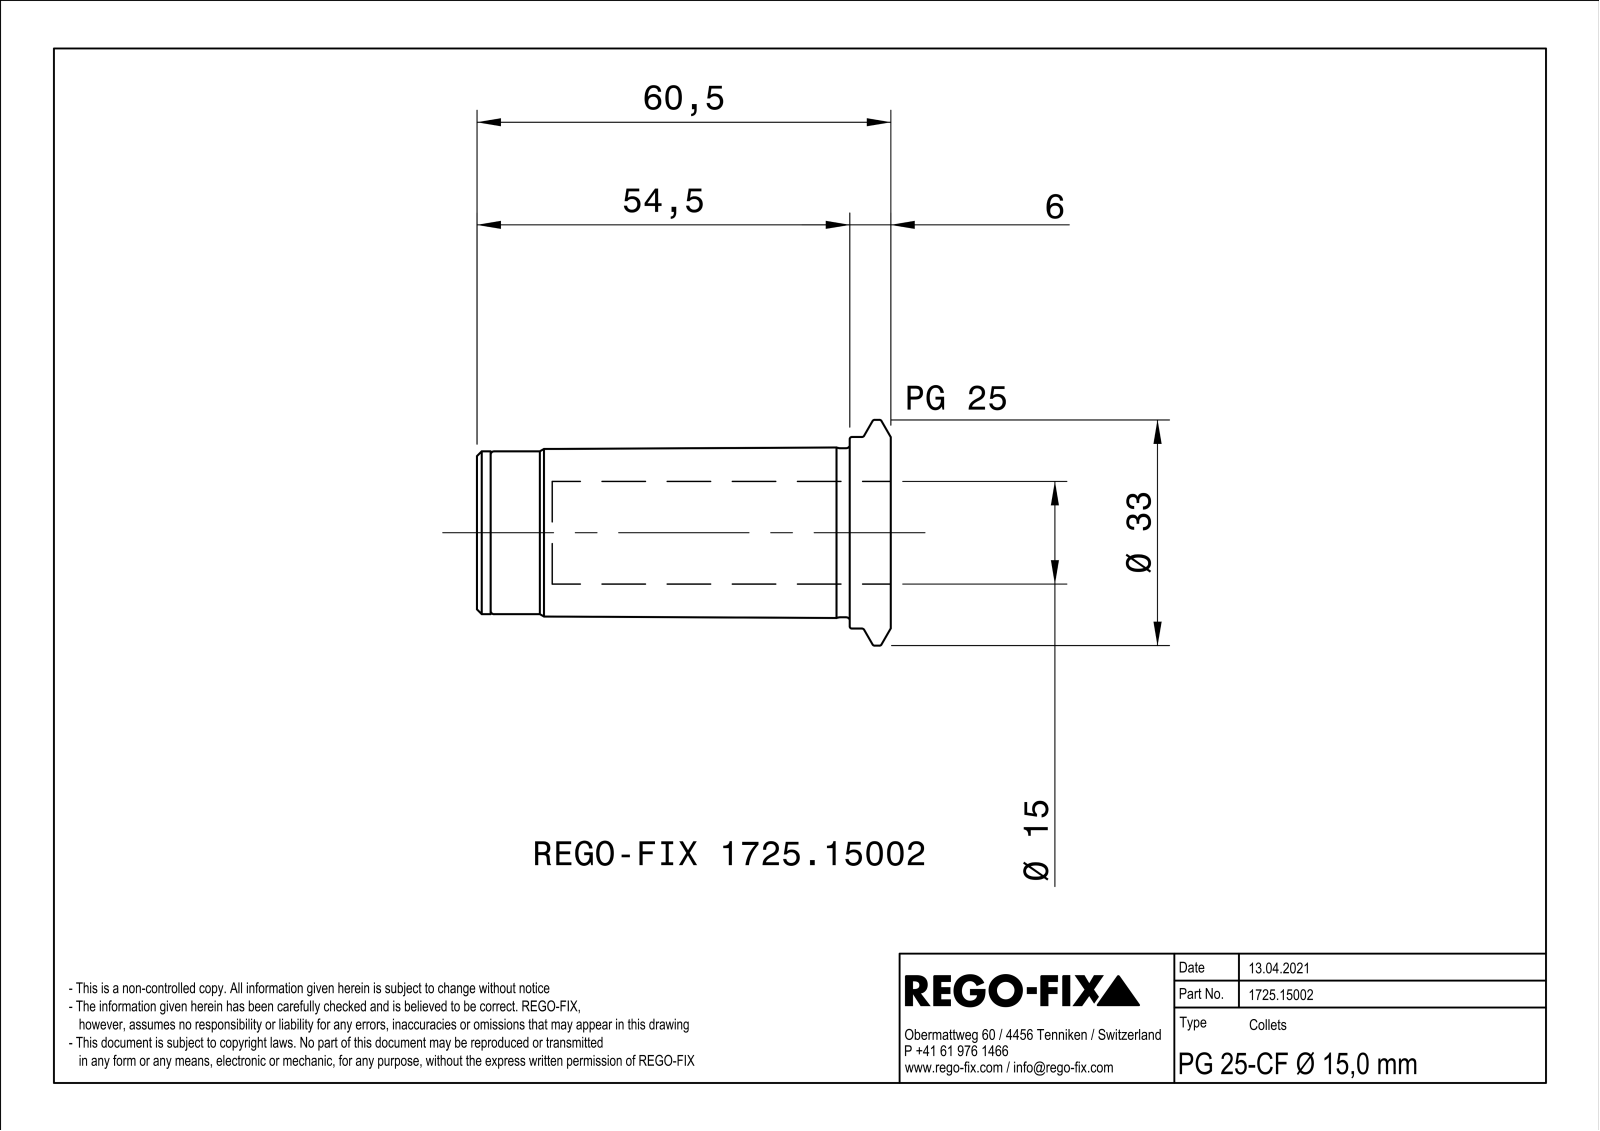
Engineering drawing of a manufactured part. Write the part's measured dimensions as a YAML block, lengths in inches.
part_name: "NOCUT"
step_written_by: "SIEMENS PLM Software Solid Edge ST10 (AUTOMOTIVE_DESIGN)"
units: inches
bodies: {solids: 1, faces: 89, planar: 23, cylindrical: 27, other: 39}
overall_size: [2.382, 1.299, 1.299]
volume: 1.173
surface_area: 17.36
round_holes:
  - {diameter: 0.098, count: 3}
  - {diameter: 0.205, count: 1}
  - {diameter: 0.272, count: 1}
  - {diameter: 0.323, count: 1}
  - {diameter: 0.591, count: 1}
  - {diameter: 0.824, count: 1}
  - {diameter: 0.874, count: 1}
round_bosses_or_shafts:
  - {diameter: 1.299, count: 1}
  - {diameter: 1.102, count: 1}
  - {diameter: 0.972, count: 1}
  - {diameter: 0.937, count: 1}
  - {diameter: 0.803, count: 1}
  - {diameter: 0.472, count: 1}
partial_cylinders:
  - {radius: 0.03, count: 3}
face_to_face_distances: [0.039, 2.382, 2.071, 0.311, 2.303, 0.232, 0.079, 1.969, 0.102, 0.335]
hole_center_spacings: [0.305, 0.529, 0.528]
